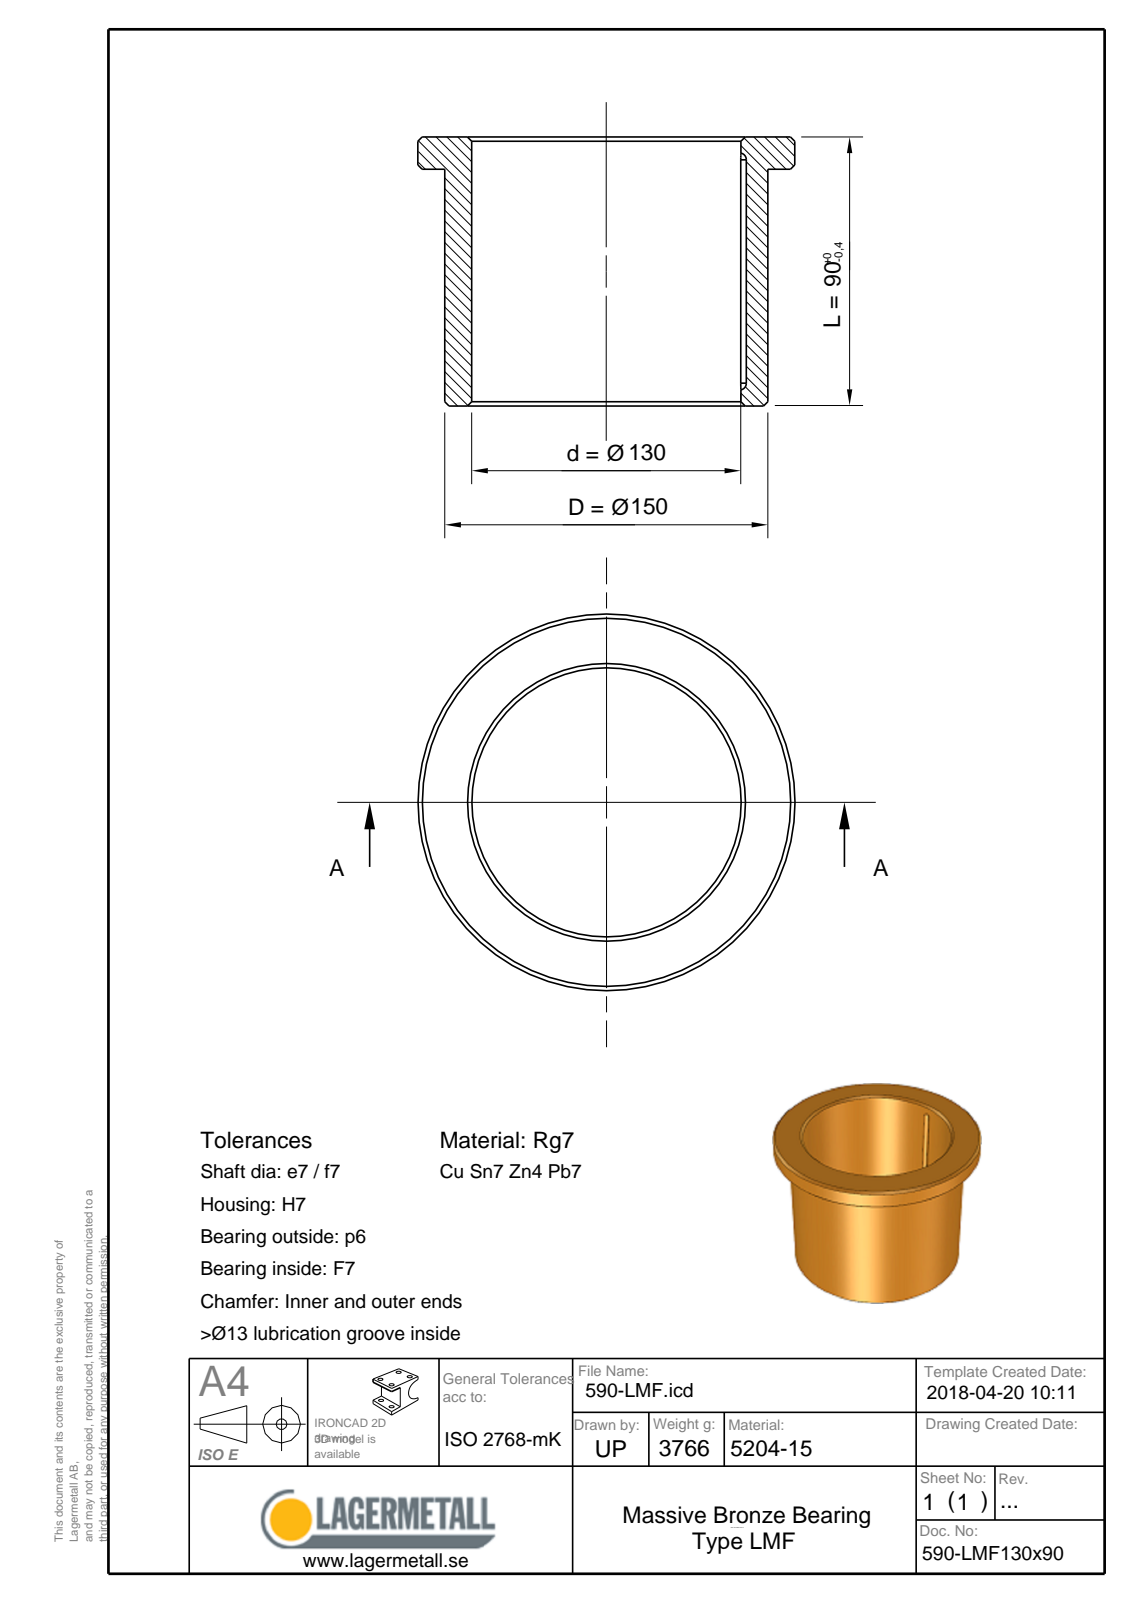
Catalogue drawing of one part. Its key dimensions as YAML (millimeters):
part_name: "590-LMF130x90"
step_written_by: "Spatial InterOp 3D (CONFIG_CONTROL_DESIGN)"
units: millimeters
bodies: {solids: 1, faces: 16, planar: 4, cylindrical: 5, other: 7}
overall_size: [165, 165, 90]
volume: 427994
surface_area: 93257
round_holes:
  - {diameter: 130, count: 1}
round_bosses_or_shafts:
  - {diameter: 165, count: 1}
  - {diameter: 150, count: 1}
partial_cylinders:
  - {radius: 1.75, count: 2}
face_to_face_distances: [10, 80, 90]
